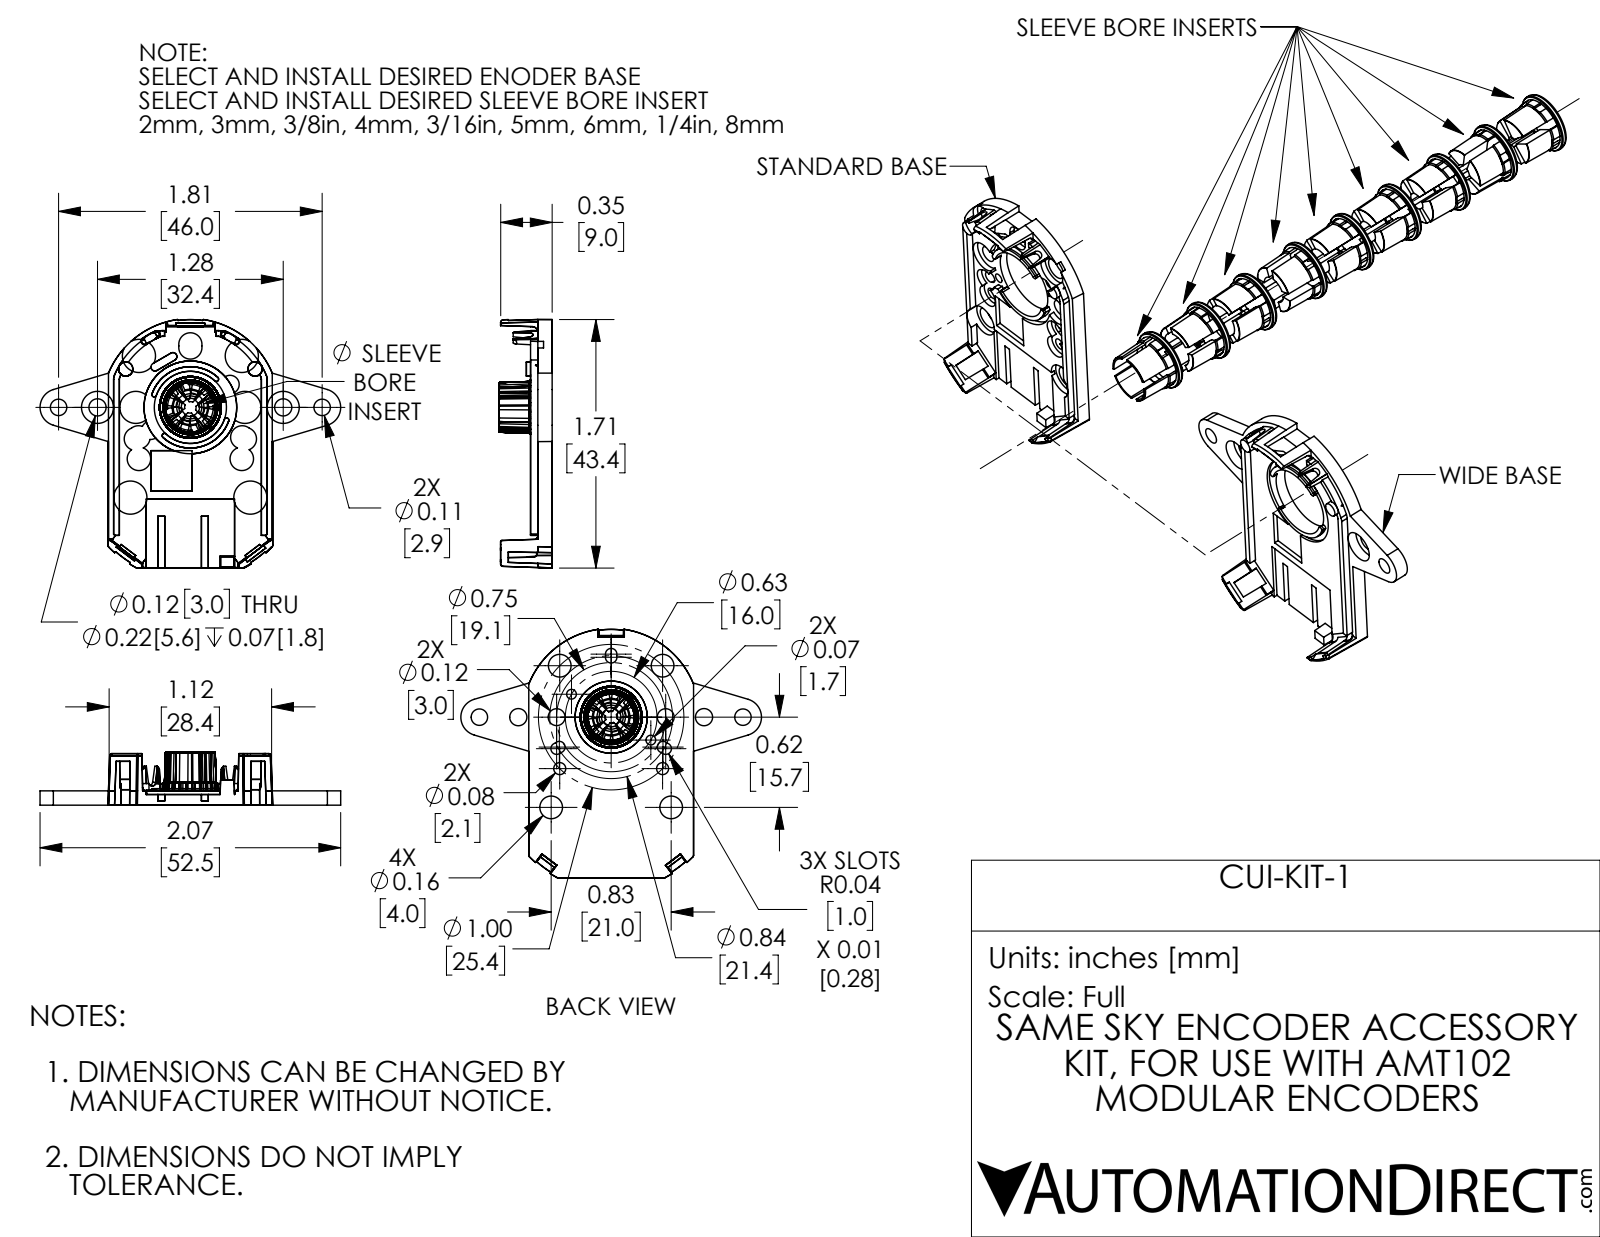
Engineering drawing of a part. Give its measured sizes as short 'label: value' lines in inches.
name: CUI-KIT-1
written by: SolidWorks 2021 (AUTOMOTIVE_DESIGN)
unit: in
bodies: 11 solids, 1439 faces (493 planar, 347 cylindrical, 599 other)
size: 4.573 × 4.035 × 1.708
volume: 0.417 in³; area: 17.54 in²
holes: 4× ⌀0.156, 4× ⌀0.228, 2× ⌀0.067, 2× ⌀0.083, 2× ⌀0.113, 2× ⌀0.116, 2× ⌀0.118, 2× ⌀0.161, 2× ⌀0.22, 2× ⌀0.496
bosses: 1× ⌀0.413, 1× ⌀0.356
rounds: 18× R0.039, 14× R0.016, 9× R0.079, 6× R0.08, 4× R0.028, 4× R0.03, 3× R0.039, 2× R0.02
face distances: 0.057, 0.098, 0.156, 0.041, 0.039, 0.029, 0.073, 0.025, 0.059, 0.097
hole spacings: 0.354, 0.5, 0.707, 0.188, 0.212, 0.273, 0.315, 0.517
